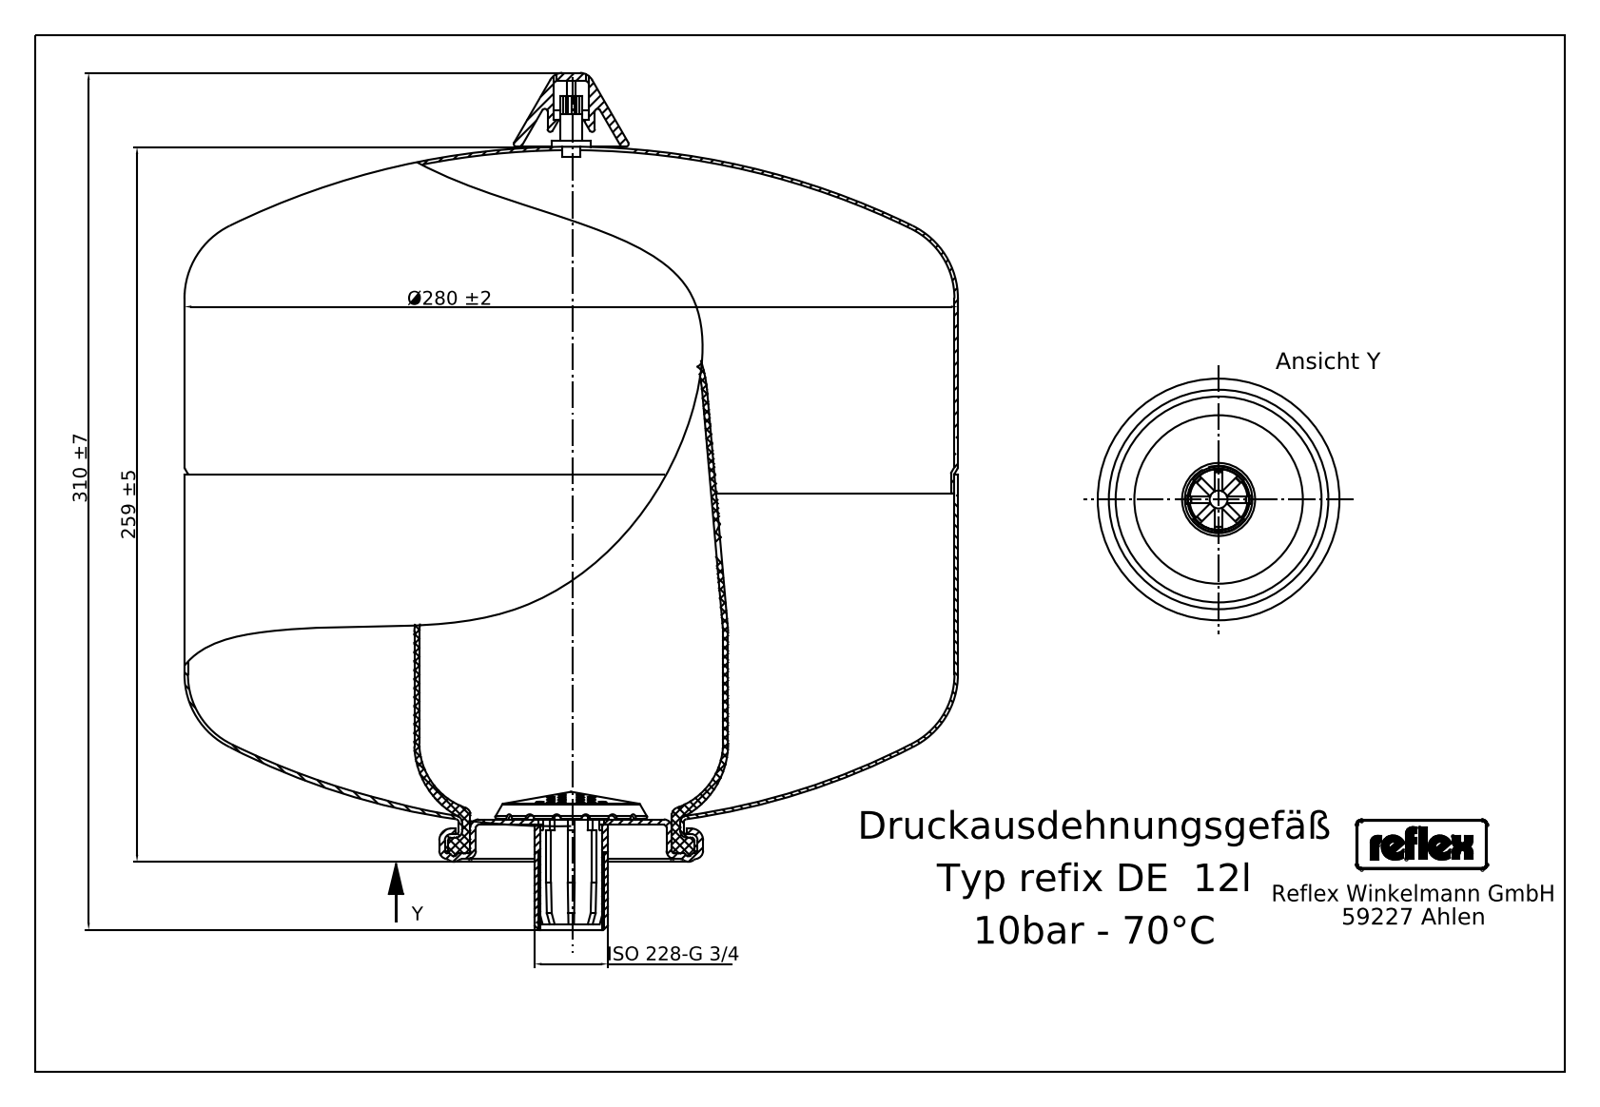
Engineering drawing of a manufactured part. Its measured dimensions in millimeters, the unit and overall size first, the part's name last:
Units: millimetres
Overall size (bounding box): 310 × 280.32 × 280
Round holes (diameter × count): ⌀14.1 ×1, ⌀18.9 ×1
Round bosses / shafts (diameter × count): ⌀280 ×1, ⌀96 ×1, ⌀82 ×1, ⌀26.9 ×1, ⌀17.1 ×1, ⌀9 ×1, ⌀6 ×1
Partial cylindrical surfaces — rounded edges, fillets, slot ends (radius × count): R1.12 ×4, R0.45 ×3, R0.77 ×2, R1.35 ×2, R1.85 ×2, R1.88 ×2, R2.54 ×2, R0.56 ×1
Main face-to-face distances: 136, 49, 185, 13, 62, 198, 129.5, 116.5, 67.5, 68.5
Volume: 12 880 000 mm³ · Surface area: 557 001 mm²
Bodies: 13 solids, 151 faces (71 planar, 46 cylindrical, 34 other)
STEP written by: Mechanical Desktop 2008 (CONFIG_CONTROL_DESIGN)
